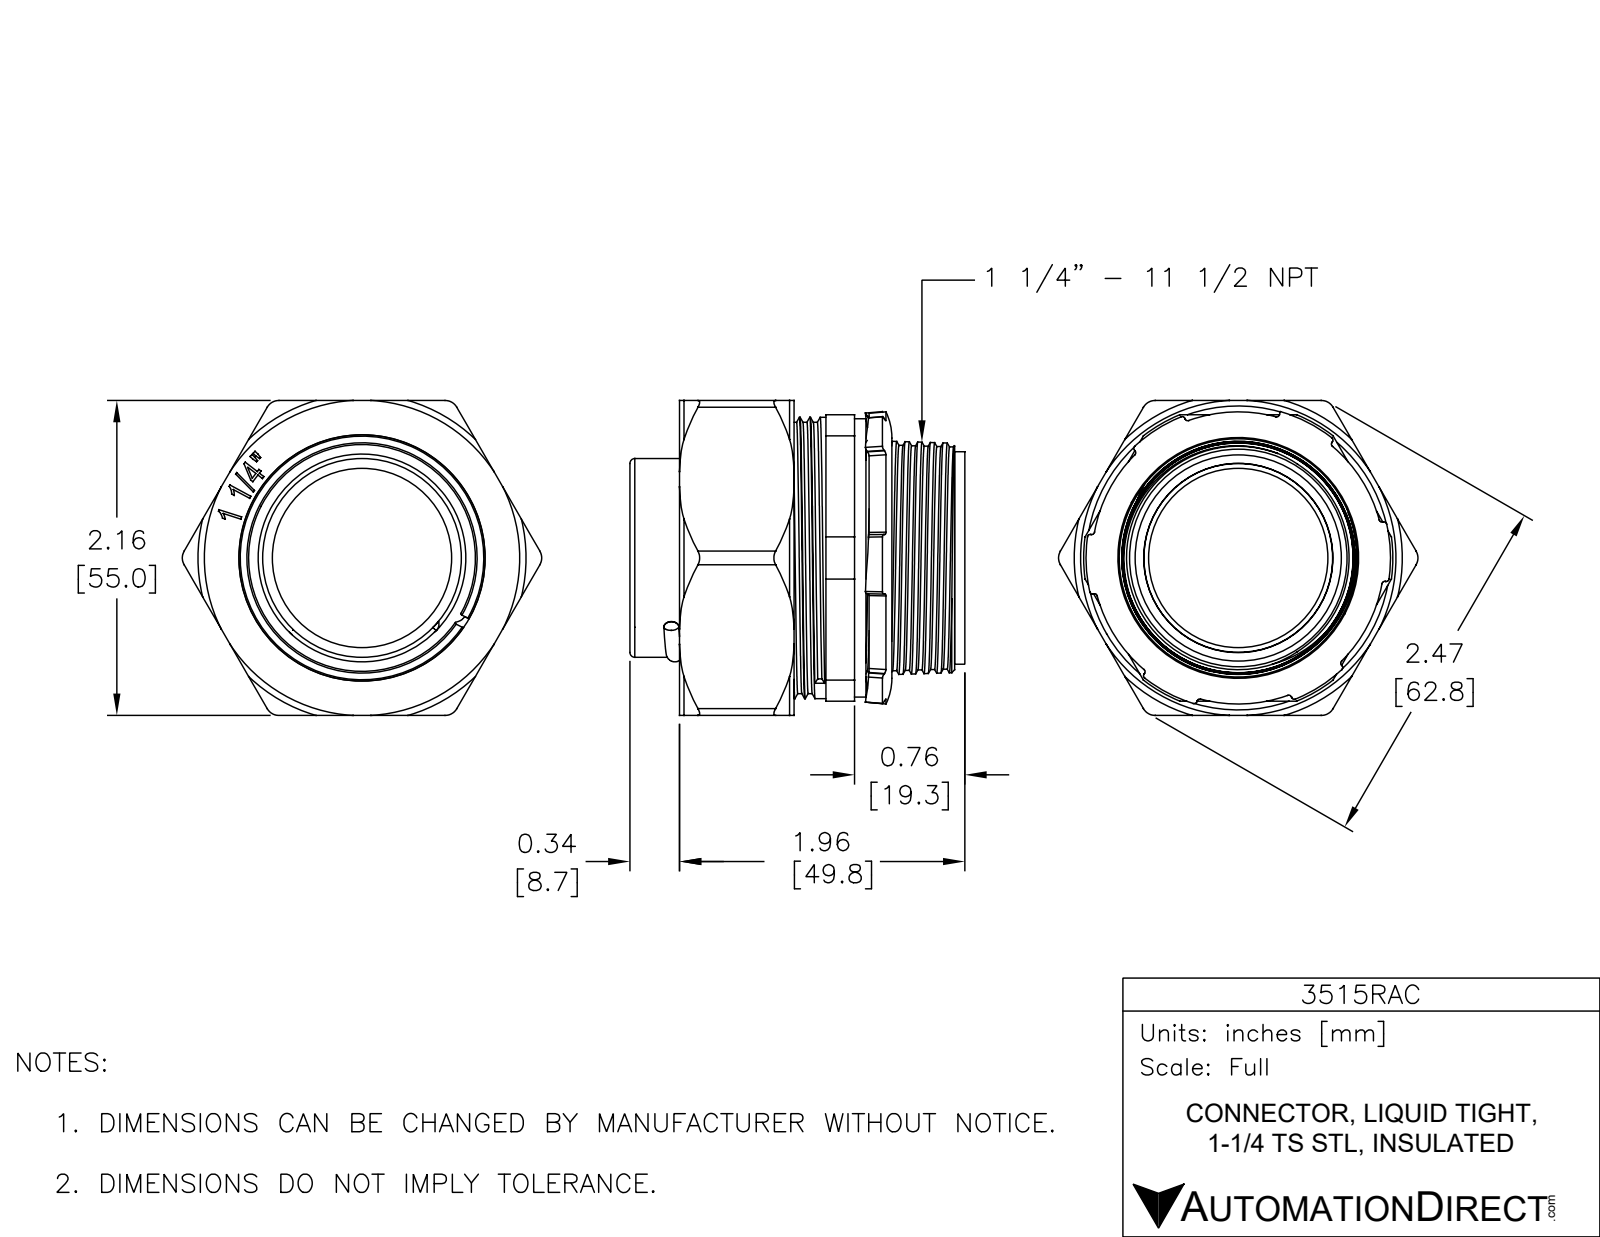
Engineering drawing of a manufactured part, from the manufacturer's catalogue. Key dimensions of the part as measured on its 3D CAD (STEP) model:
Part name (STEP PRODUCT): 3515RAC
STEP written by: SolidWorks 2018 (AUTOMOTIVE_DESIGN)
Units: inches
Bodies: 7 solids, 533 faces (215 planar, 128 cylindrical, 190 other)
Overall size (bounding box): 2.471 × 2.304 × 2.165
Volume: 2.555 in³ · Surface area: 68.9 in²
Round holes (diameter × count): ⌀0.182 ×1, ⌀1.232 ×1, ⌀1.26 ×1, ⌀1.3 ×1, ⌀1.417 ×1, ⌀1.555 ×1, ⌀1.638 ×1, ⌀1.666 ×1, ⌀1.693 ×1, ⌀1.76 ×1, ⌀1.909 ×1
Round bosses / shafts (diameter × count): ⌀1.934 ×1, ⌀1.913 ×1, ⌀1.87 ×1, ⌀1.865 ×1, ⌀1.732 ×1, ⌀1.465 ×1, ⌀1.366 ×1, ⌀1.298 ×1
Partial cylindrical surfaces — rounded edges, fillets, slot ends (radius × count): R0.012 ×8, R0.094 ×6, R0.004 ×2, R0.052 ×2, R0.006 ×1, R0.015 ×1, R0.023 ×1, R1.063 ×1
Main face-to-face distances: 2.165, 1.203, 0.098, 2.067, 1.282, 0.079, 0.928, 0.275, 0.354, 1.969
Hole centre spacings: 0.965
